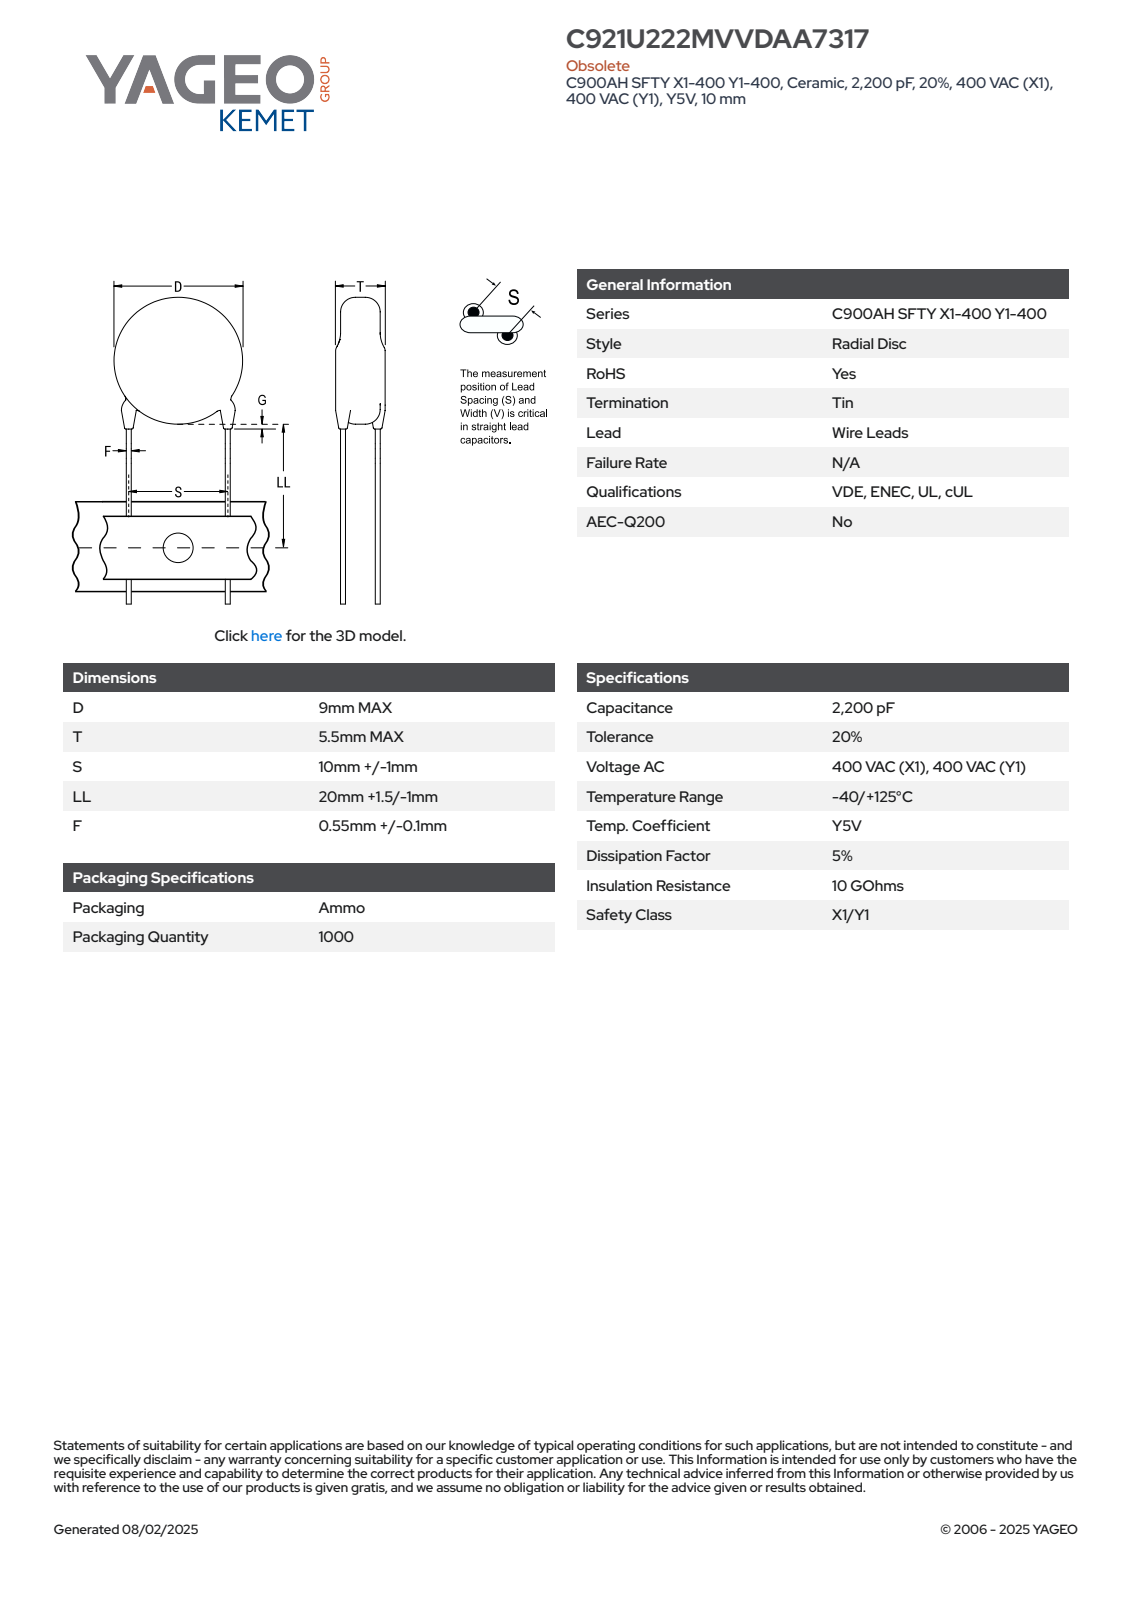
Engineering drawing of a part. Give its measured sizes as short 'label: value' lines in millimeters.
name: CCD_STC900_D9T5.5S10LL21.5F0.65G3
written by: SolidWorks 2014 (AUTOMOTIVE_DESIGN)
unit: mm
bodies: 4 solids, 83 faces (61 planar, 6 cylindrical, 16 other)
size: 30.5 × 9.47 × 5.88
volume: 356 mm³; area: 364 mm²
bosses: 2× ⌀0.65, 1× ⌀9
face distances: 5.5, 1.04, 26.52, 25.48, 0.84, 0.45, 0.39, 2.14, 3.08, 3.2
